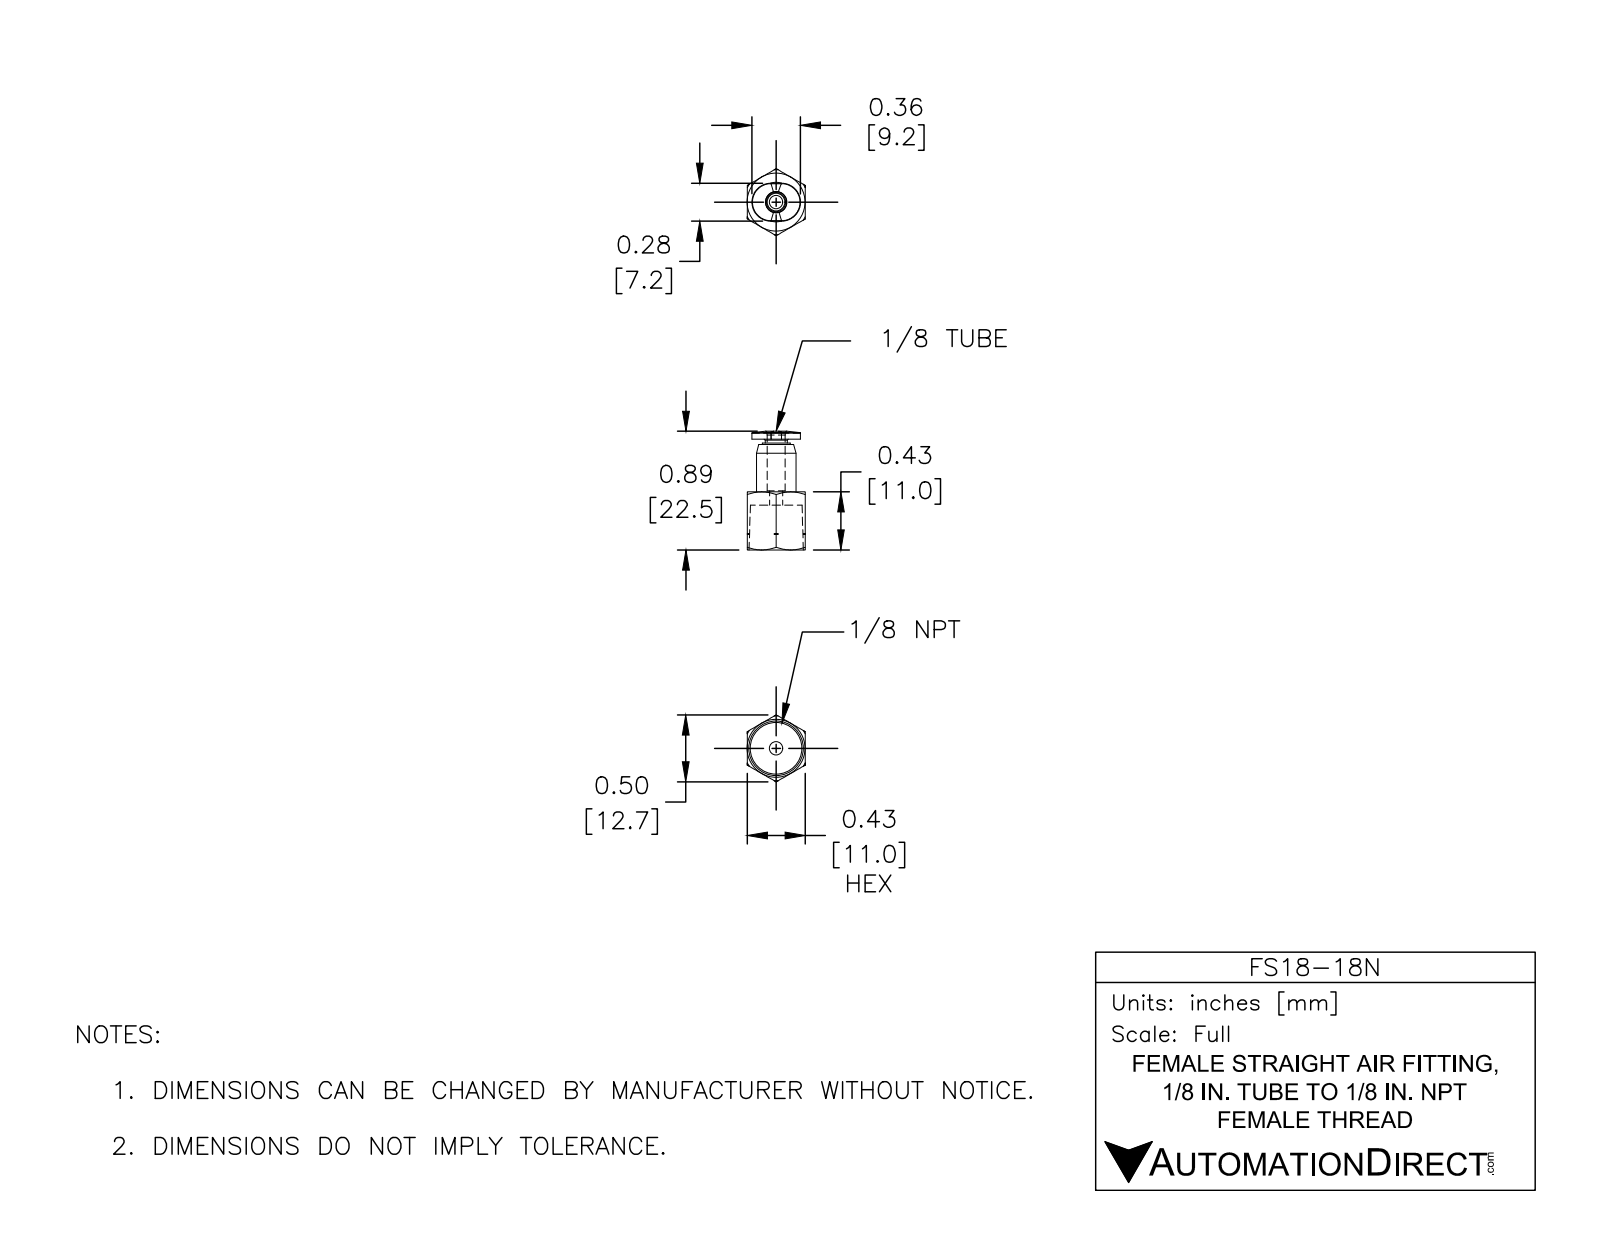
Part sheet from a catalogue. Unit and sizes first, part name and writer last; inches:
Units: inches
Overall size (bounding box): 0.886 × 0.5 × 0.433
Round holes (diameter × count): ⌀0.098 ×1, ⌀0.134 ×1
Round bosses / shafts (diameter × count): ⌀0.295 ×1, ⌀0.209 ×1, ⌀0.165 ×1
Partial cylindrical surfaces — rounded edges, fillets, slot ends (radius × count): R0.142 ×2
Main face-to-face distances: 0.433, 0.098, 0.492, 0.394, 0.453, 0.354, 0.039, 0.335, 0.787, 0.827
Volume: 0.051 in³ · Surface area: 2.074 in²
Bodies: 1 solid, 78 faces (16 planar, 12 cylindrical, 50 other)
Part name (STEP PRODUCT): FS18-18N
STEP written by: SolidWorks 2015 (CONFIG_CONTROL_DESIGN)
